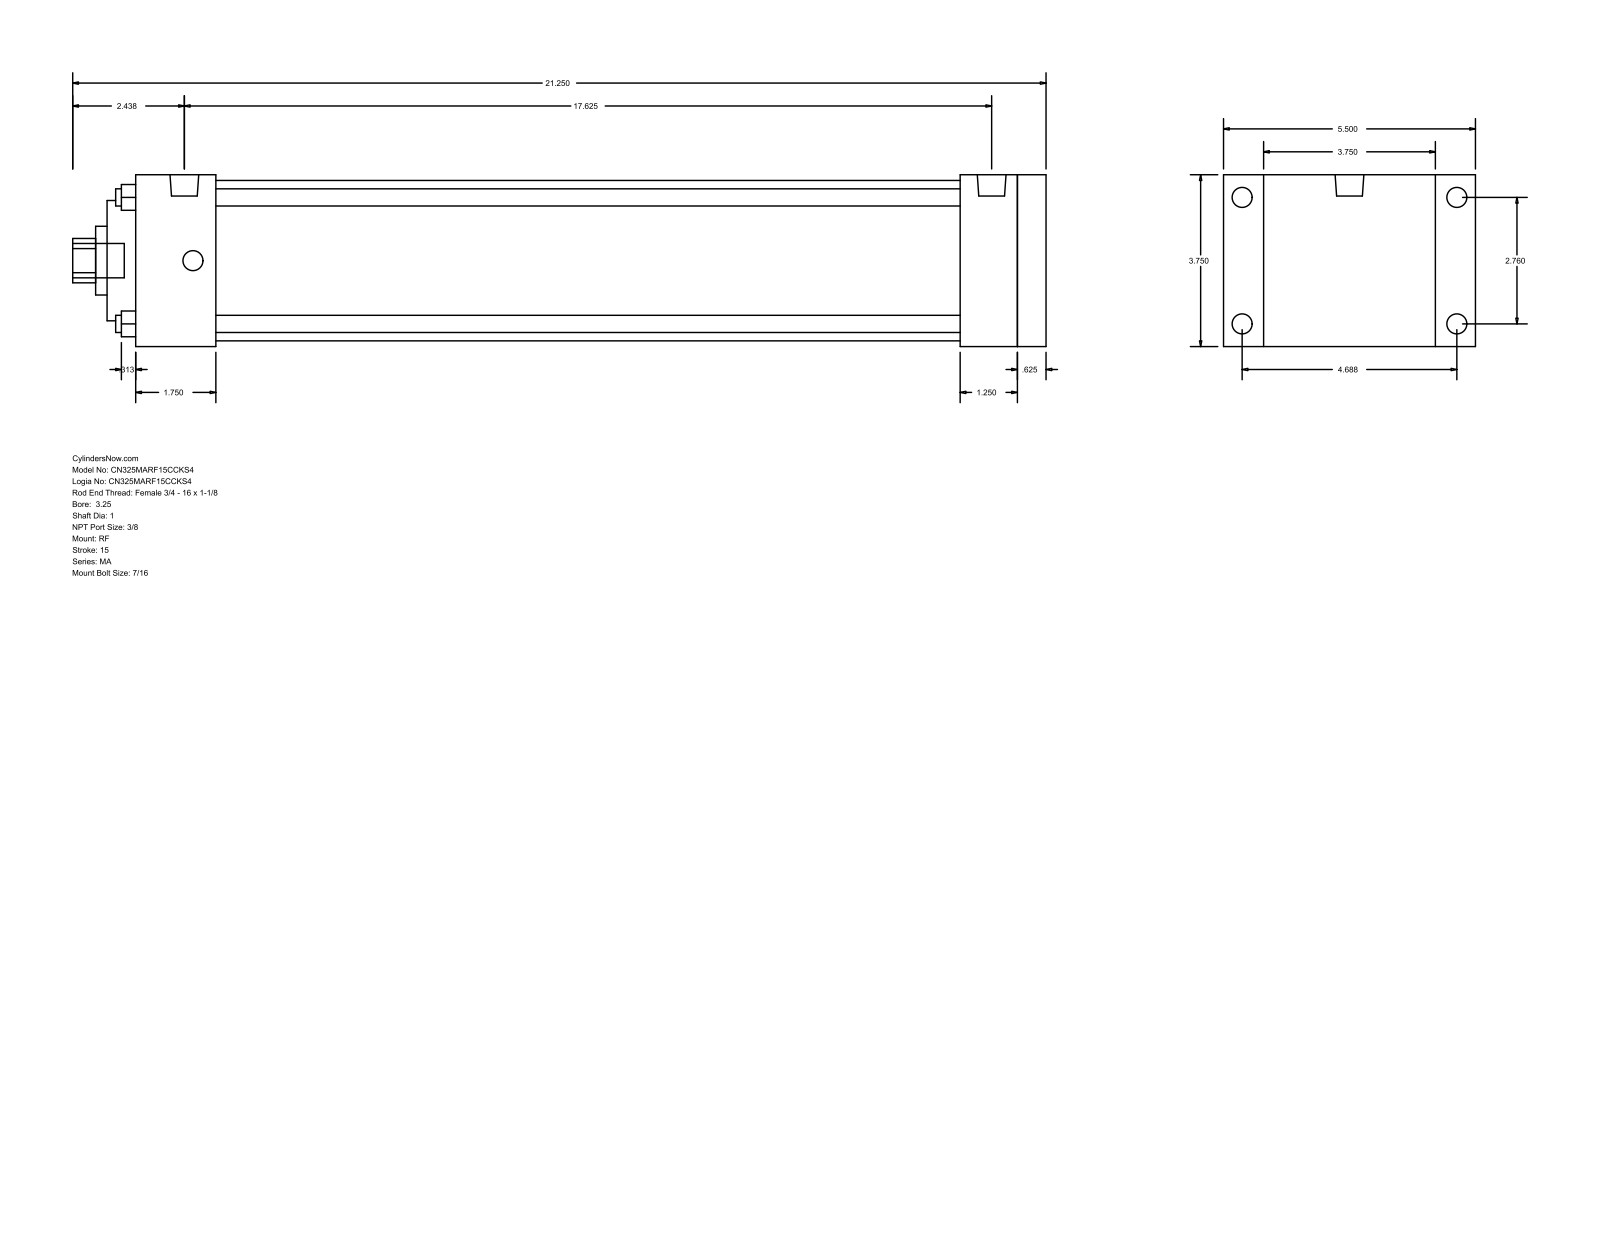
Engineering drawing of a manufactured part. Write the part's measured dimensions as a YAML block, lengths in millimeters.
part_name: "MA_RF__0325_1"
step_written_by: "GSSL Pune (CONFIG_CONTROL_DESIGN)"
units: millimeters
bodies: {solids: 0, faces: 94, planar: 65, cylindrical: 29, other: 0}
overall_size: [539.75, 139.7, 95.25]
round_holes:
  - {diameter: 9.53, count: 4}
  - {diameter: 25.4, count: 1}
  - {diameter: 38.1, count: 1}
  - {diameter: 66.67, count: 1}
  - {diameter: 88.9, count: 1}
round_bosses_or_shafts:
  - {diameter: 11.11, count: 8}
  - {diameter: 15.93, count: 2}
  - {diameter: 19.05, count: 1}
partial_cylinders:
  - {radius: 12.29, count: 1}
face_to_face_distances: [95.24, 504.83, 15.87, 488.96, 22.23, 117.47, 457.2, 31.76, 47.63, 44.46]
hole_center_spacings: [49.57, 70.1, 99.14]
